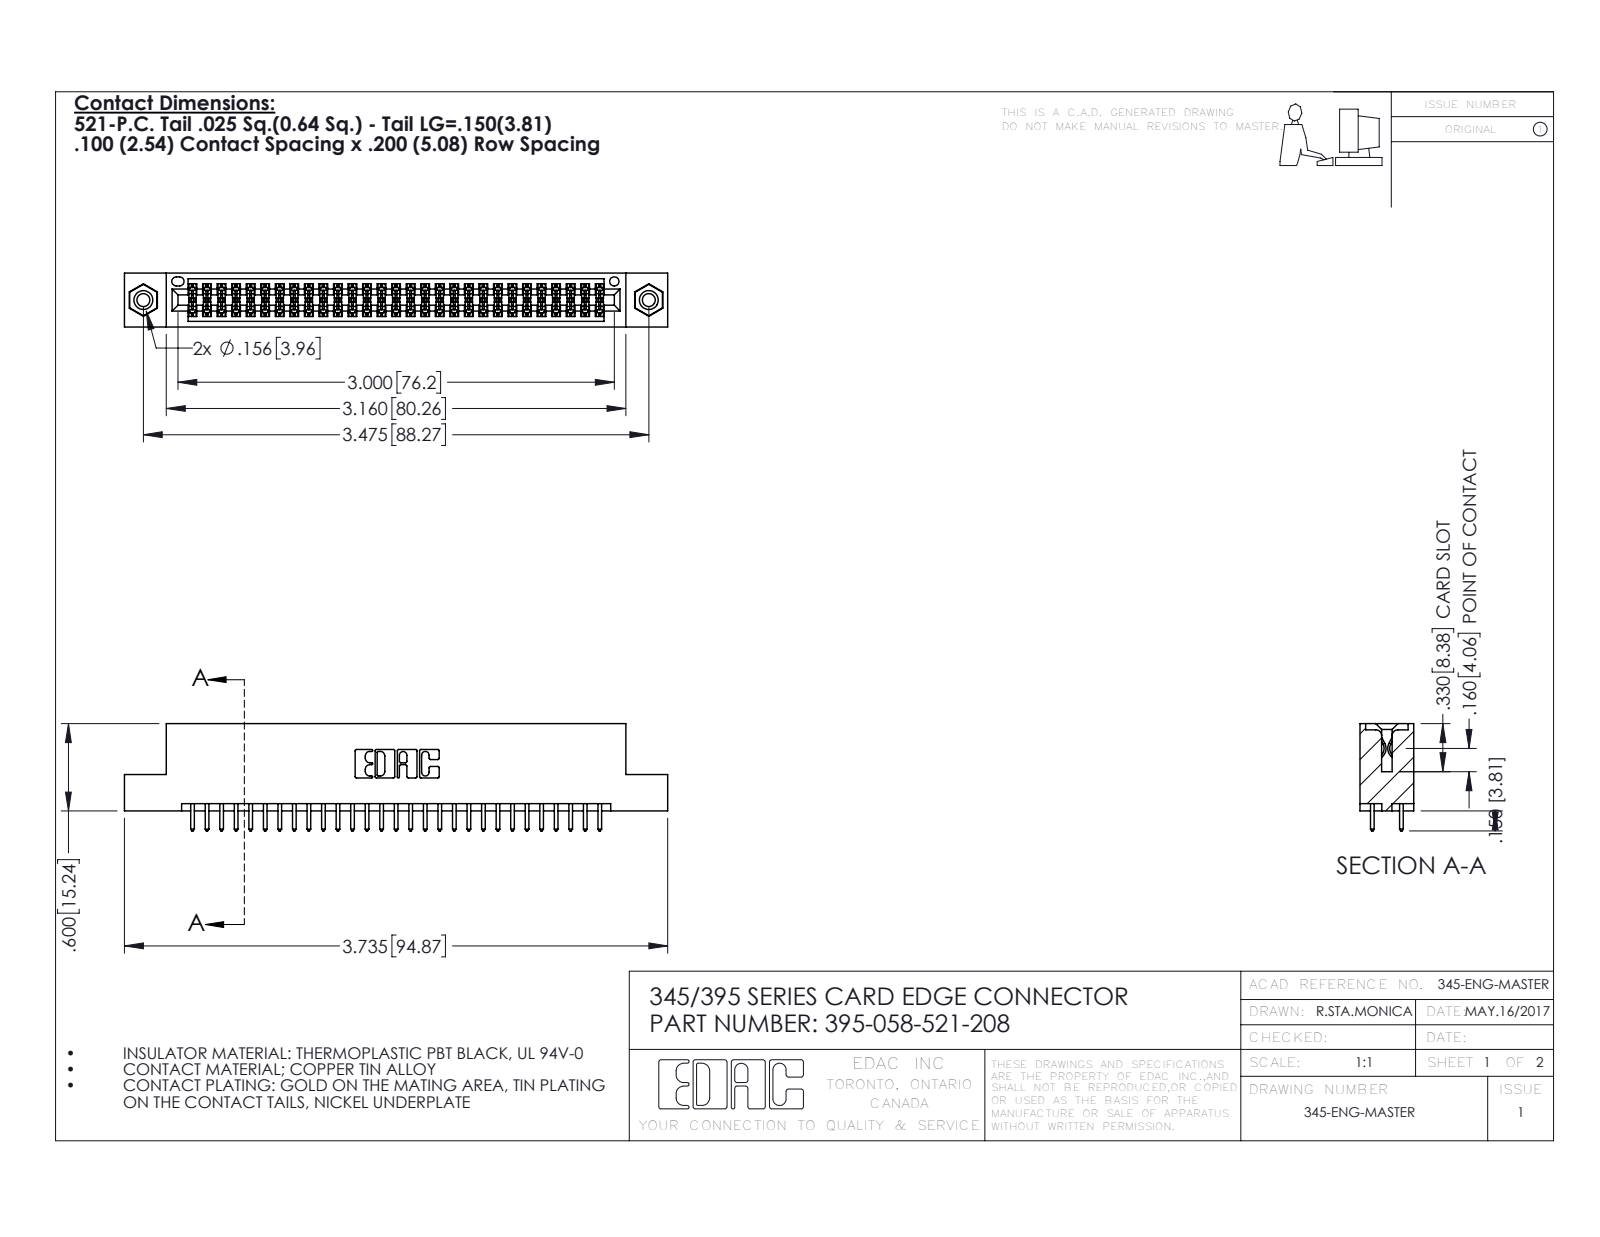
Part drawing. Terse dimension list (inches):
name: 345 Part_Flush Mounting Lugs - 0.156 Dia-TI; 345-292-001_345-293-121; 395-058-521-208; 345-250-001_345-250-003-102
written by: SolidWorks 2016 (CONFIG_CONTROL_DESIGN)
unit: in
bodies: 61 solids, 3086 faces (2026 planar, 1044 cylindrical, 16 other)
size: 3.735 × 0.737 × 0.37
volume: 0.553 in³; area: 20.16 in²
holes: 2× ⌀0.089, 2× ⌀0.125, 2× ⌀0.156, 1× ⌀0.064
bosses: 2× ⌀0.155
rounds: 87× R0.006, 58× R0.01, 22× R0.01, 6× R0.007, 6× R0.031, 3× R0.026, 2× R0.014, 2× R0.019
face distances: 0.072, 0.298, 0.2, 0.37, 0.098, 0.272, 0.025, 0.225, 0.175, 0.149
hole spacings: 0.27, 3.24, 3.475
